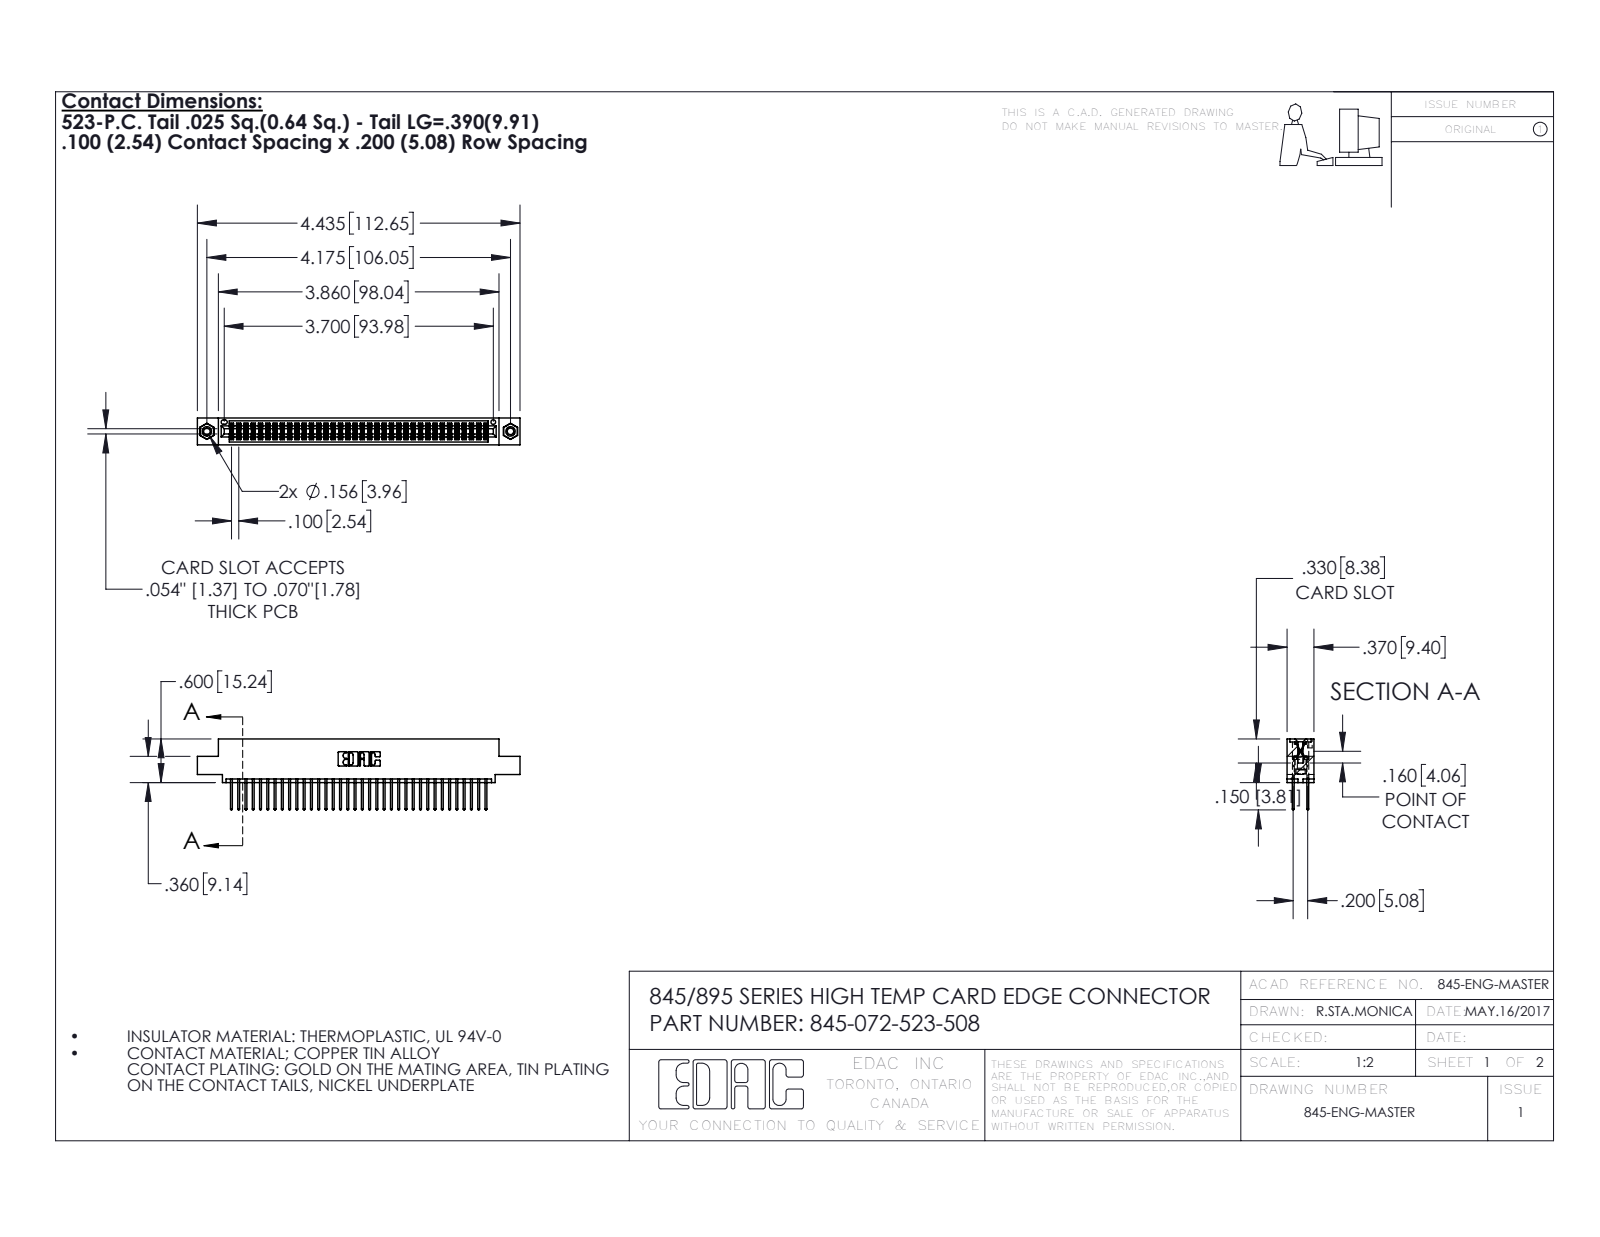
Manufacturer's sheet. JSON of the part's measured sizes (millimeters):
{"part_name": "345-250-001_345-250-003-102; 345-072-523-508; 345-292-001_345-293-123; 345 Part_0.110 Offset - 0.156 Dia-TI", "step_written_by": "SolidWorks 2016 (CONFIG_CONTROL_DESIGN)", "units": "millimeters", "bodies": {"solids": 75, "faces": 3790, "planar": 2492, "cylindrical": 1282, "other": 16}, "overall_size": [112.6, 24.8, 9.4], "volume_mm3": 11000, "surface_area_mm2": 16850, "round_holes": [[2.3, 2], [3.2, 2], [4, 2], [1.6, 1]], "round_bosses_or_shafts": [[3.9, 2]], "partial_cylinders_radius": [[0.2, 108], [0.3, 72], [0.3, 22], [0.2, 6], [0.8, 6], [0.7, 3], [0.4, 2], [0.5, 2]], "face_to_face_distances": [1.8, 7.6, 5.1, 2.5, 6.9, 0.6, 9.4, 5.7, 4.4, 3.8], "hole_center_spacings": [6.9, 100.1, 106]}
